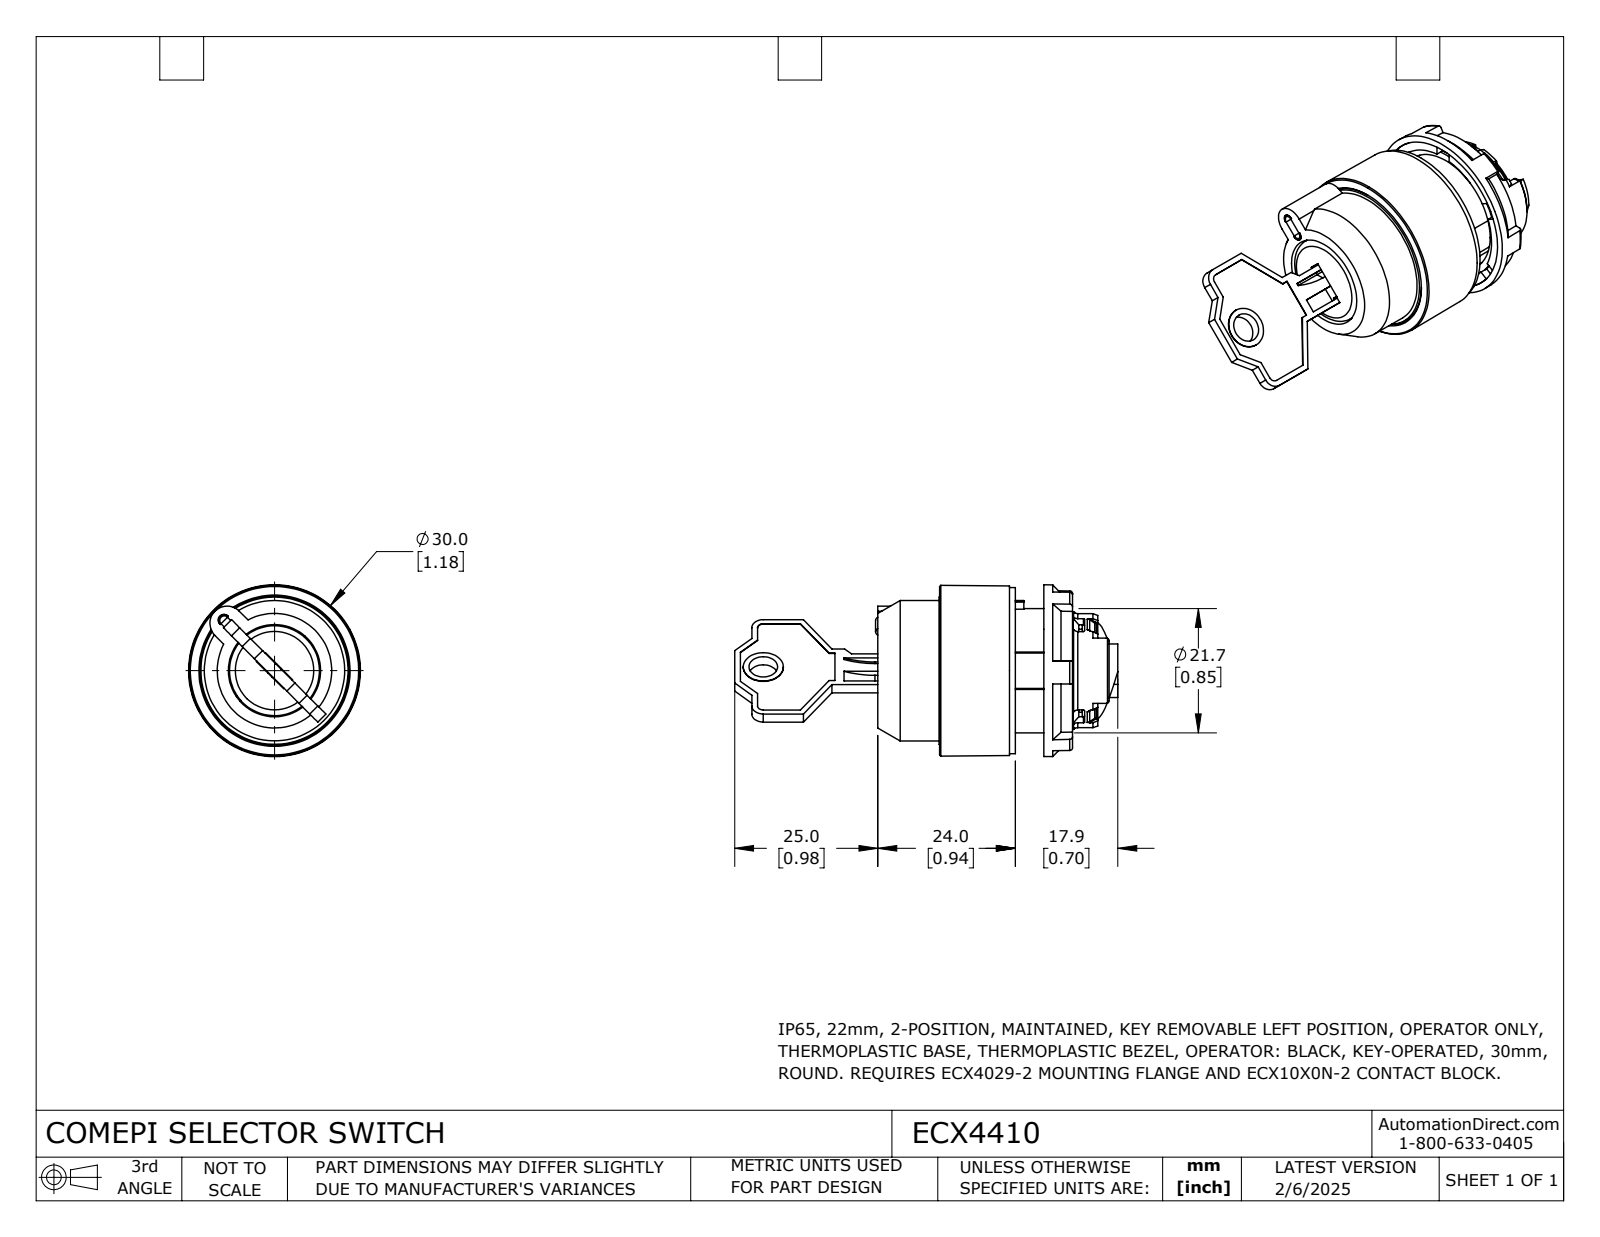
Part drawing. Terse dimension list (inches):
name: ECX4410
written by: SolidWorks 2024 (CONFIG_CONTROL_DESIGN)
unit: in
bodies: 3 solids, 563 faces (247 planar, 165 cylindrical, 151 other)
size: 2.634 × 1.181 × 1.181
volume: 0.959 in³; area: 22.79 in²
holes: 1× ⌀0.094, 1× ⌀0.13, 1× ⌀0.197, 1× ⌀0.243, 1× ⌀0.346, 1× ⌀0.5, 1× ⌀0.634, 1× ⌀0.713, 1× ⌀0.75, 1× ⌀0.752, 1× ⌀0.854, 1× ⌀0.866
bosses: 1× ⌀1.142, 1× ⌀1.012, 1× ⌀0.965, 1× ⌀0.85, 1× ⌀0.807, 1× ⌀0.787, 1× ⌀0.689, 1× ⌀0.681
rounds: 24× R0.008, 8× R0.039, 4× R0.02, 2× R0.01, 2× R0.012, 2× R0.079, 2× R0.591, 1× R0.056
face distances: 0.079, 0.039, 0.075, 0.118, 0.071, 0.197, 0.083, 0.945, 0.906, 0.827
